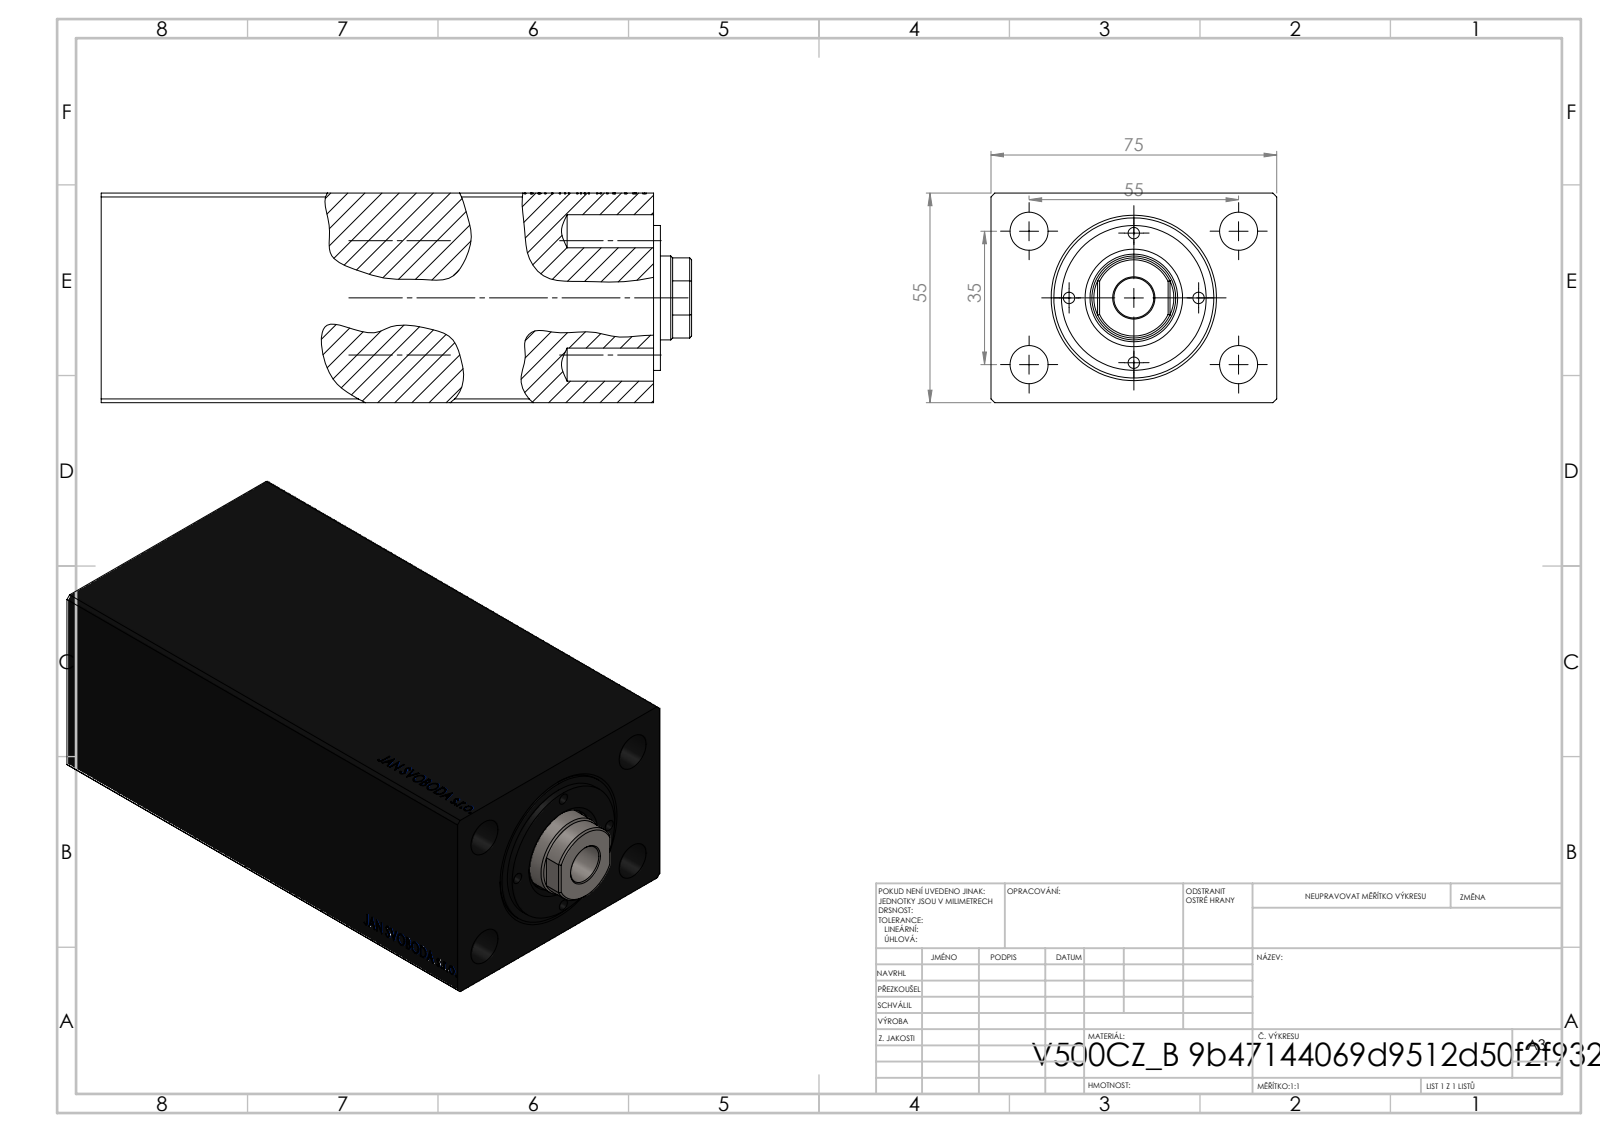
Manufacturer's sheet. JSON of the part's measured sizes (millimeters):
{"part_name": "V500CZ; V500CZ_B_VC", "step_written_by": "SolidWorks 2019 (CONFIG_CONTROL_DESIGN)", "units": "millimeters", "bodies": {"solids": 3, "faces": 873, "planar": 399, "cylindrical": 58, "other": 416}, "overall_size": [155, 75, 55], "volume_mm3": 563734, "surface_area_mm2": 96619, "round_holes": [[3, 4], [10, 4], [5.5, 2], [13.16, 2], [20, 2], [10.5, 1], [22, 1], [23, 1], [32, 1], [36, 1], [42, 1]], "round_bosses_or_shafts": [[38, 1]], "partial_cylinders_radius": [[10.5, 1]], "face_to_face_distances": [55, 75, 145, 131.5, 13.5, 66.5, 65, 80, 144.8, 79.8], "hole_center_spacings": [17, 20.41, 24.04, 27.5, 32.6, 44.12, 47.82, 34]}
